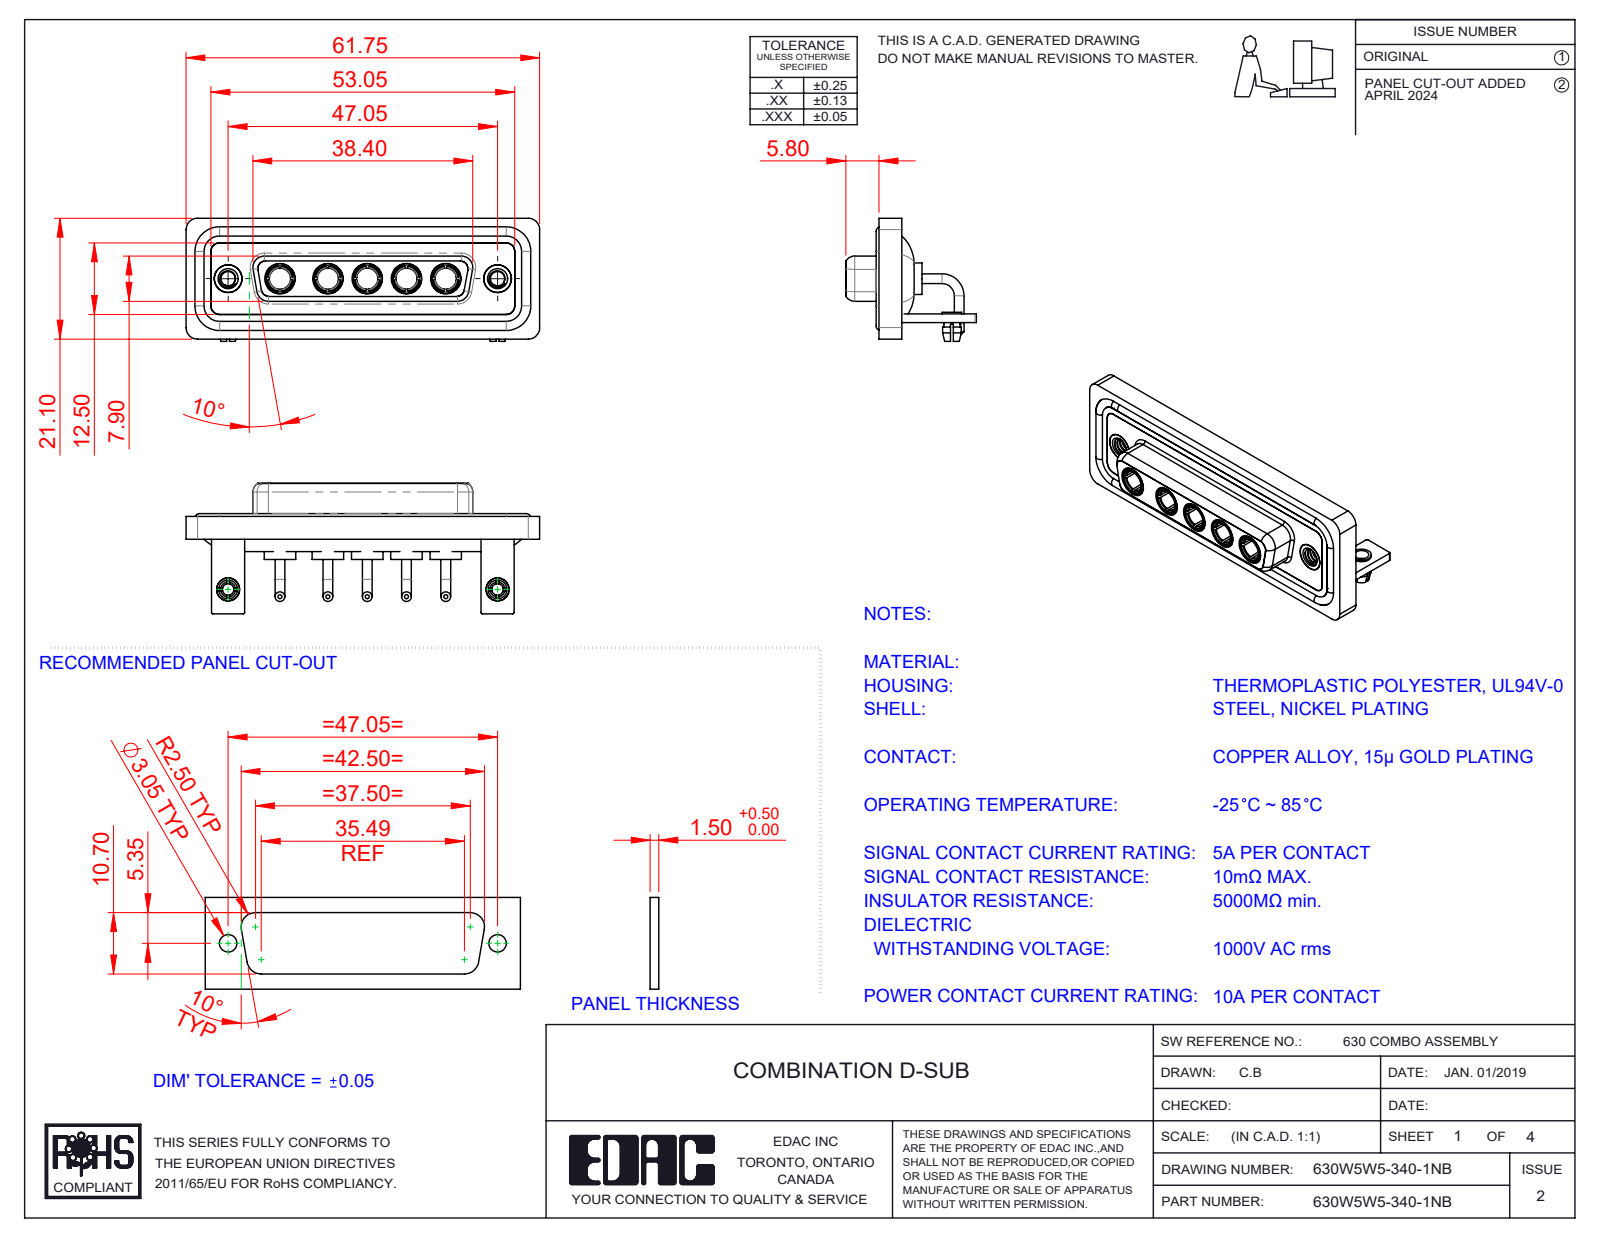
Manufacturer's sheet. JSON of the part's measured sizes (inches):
{"part_name": "630W5W5-340-1NB; 630Combo Housing_5W5; 630Combo Shell Front_25 Contacts; 630Combo Waterproof Housing_25 Contacts (+5 more)", "step_written_by": "SolidWorks 2023 (CONFIG_CONTROL_DESIGN)", "units": "inches", "bodies": {"solids": 21, "faces": 910, "planar": 318, "cylindrical": 367, "other": 225}, "overall_size": [2.431, 0.898, 0.846], "volume_in3": 0.521, "surface_area_in2": 22.49, "round_holes": [[0.191, 7], [0.146, 5], [0.209, 5], [0.098, 4], [0.079, 2], [0.126, 2], [0.157, 2], [0.159, 2], [0.197, 2]], "round_bosses_or_shafts": [[0.067, 10], [0.217, 5], [0.205, 5], [0.195, 5], [0.187, 5], [0.148, 5], [0.063, 4], [0.195, 2]], "partial_cylinders_radius": [[0.079, 19], [0.059, 18], [0.01, 16], [0.053, 8], [0.063, 8], [0.02, 5], [0.083, 5], [0.024, 4]], "face_to_face_distances": [0.016, 0.071, 0.059, 0.114, 0.146, 0.161, 0.043, 0.055, 0.063, 0.098], "hole_center_spacings": [0.27, 0.356, 1.496, 1.852, 0.27, 0.33, 0.54, 0.541]}
